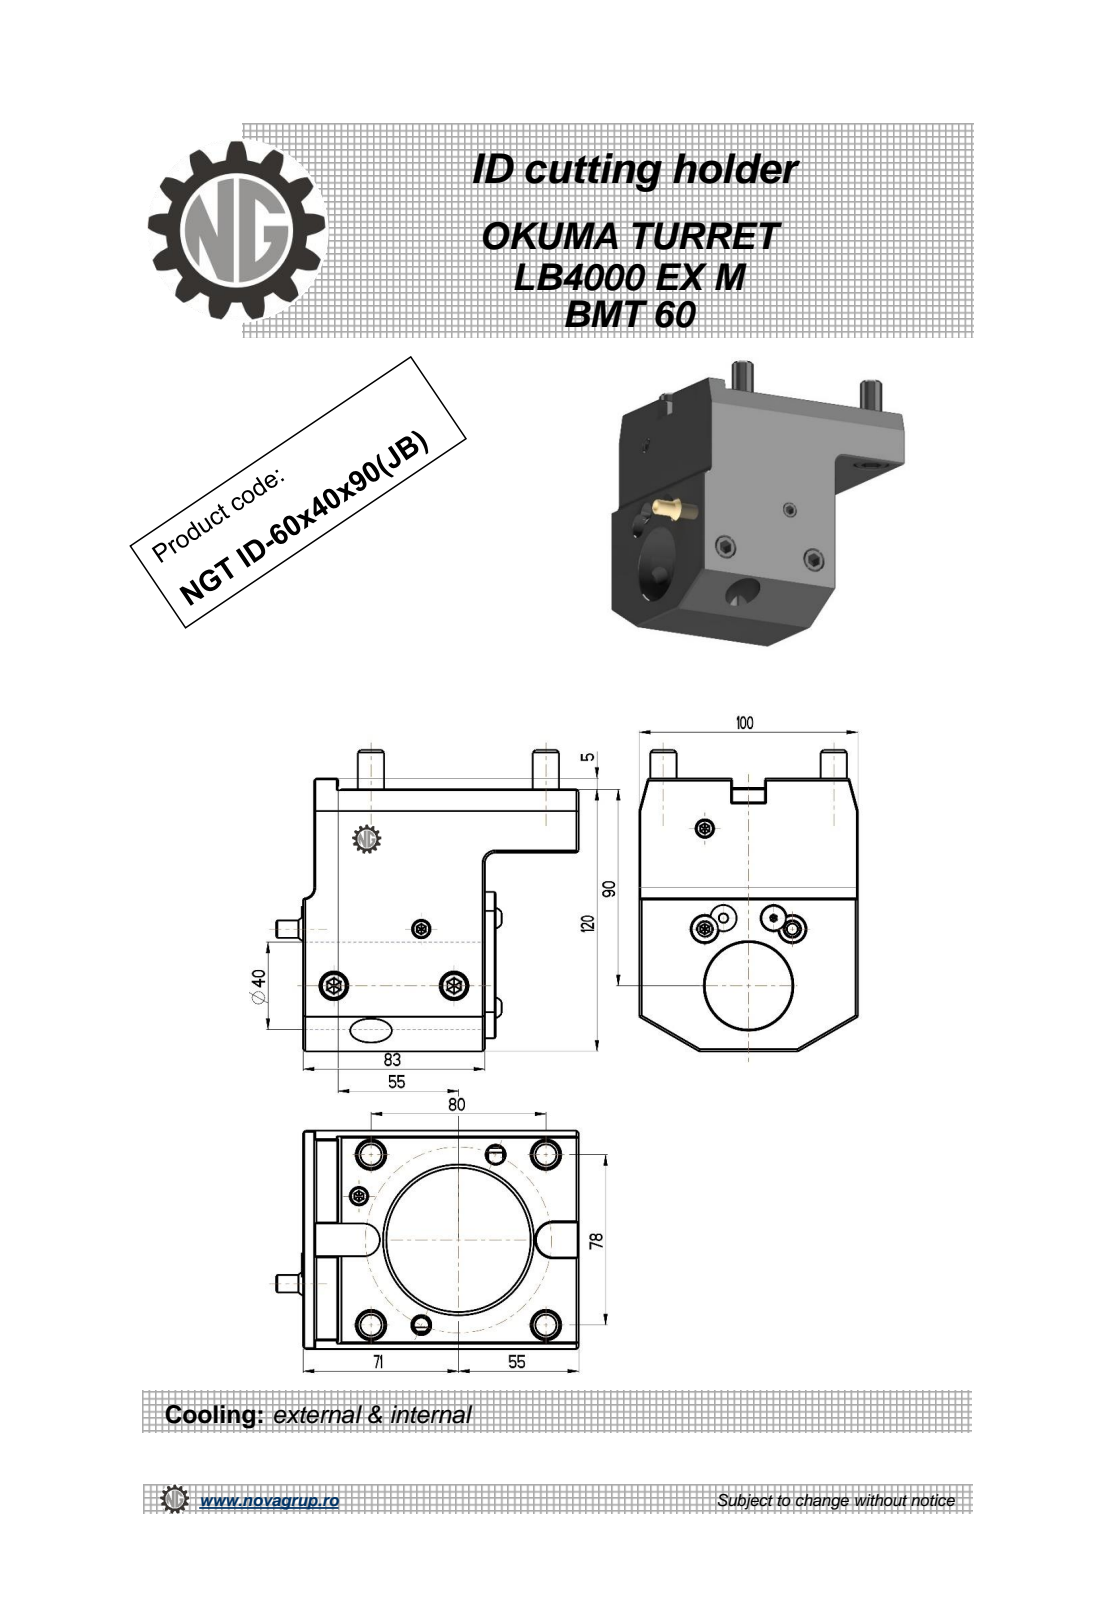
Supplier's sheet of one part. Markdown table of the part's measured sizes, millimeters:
| quantity | value |
| --- | --- |
| part name | NGT_ID_60_40_90_JB |
| STEP written by | PRO/ENGINEER BY PARAMETRIC TECHNOLOGY CORPORATION, 2010280 (CONFIG_CONTROL_DESIGN) |
| units | millimeters |
| bodies | 1 solid, 284 faces (129 planar, 68 cylindrical, 87 other) |
| overall size | 138.34 × 138 × 100 |
| volume | 970 425 mm³ |
| surface area | 89 989 mm² |
| round holes (diameter × count) | 8.2 × 2, 10.2 × 2, 5 × 1, 6.8 × 1, 40 × 1, 69 × 1 |
| round bosses / shafts (diameter × count) | 12 × 4, 61 × 1, 11.2 × 1, 8 × 1 |
| partial cylindrical surfaces (radius × count) | 0.61 × 24, 0.22 × 6, 5 × 2, 4 × 1, 7.5 × 1, 8 × 1 |
| main face-to-face distances | 5, 83, 100, 78, 29, 120, 91, 88, 38, 126 |
| hole center spacings | 42.54, 32.8, 55, 85.09 |
